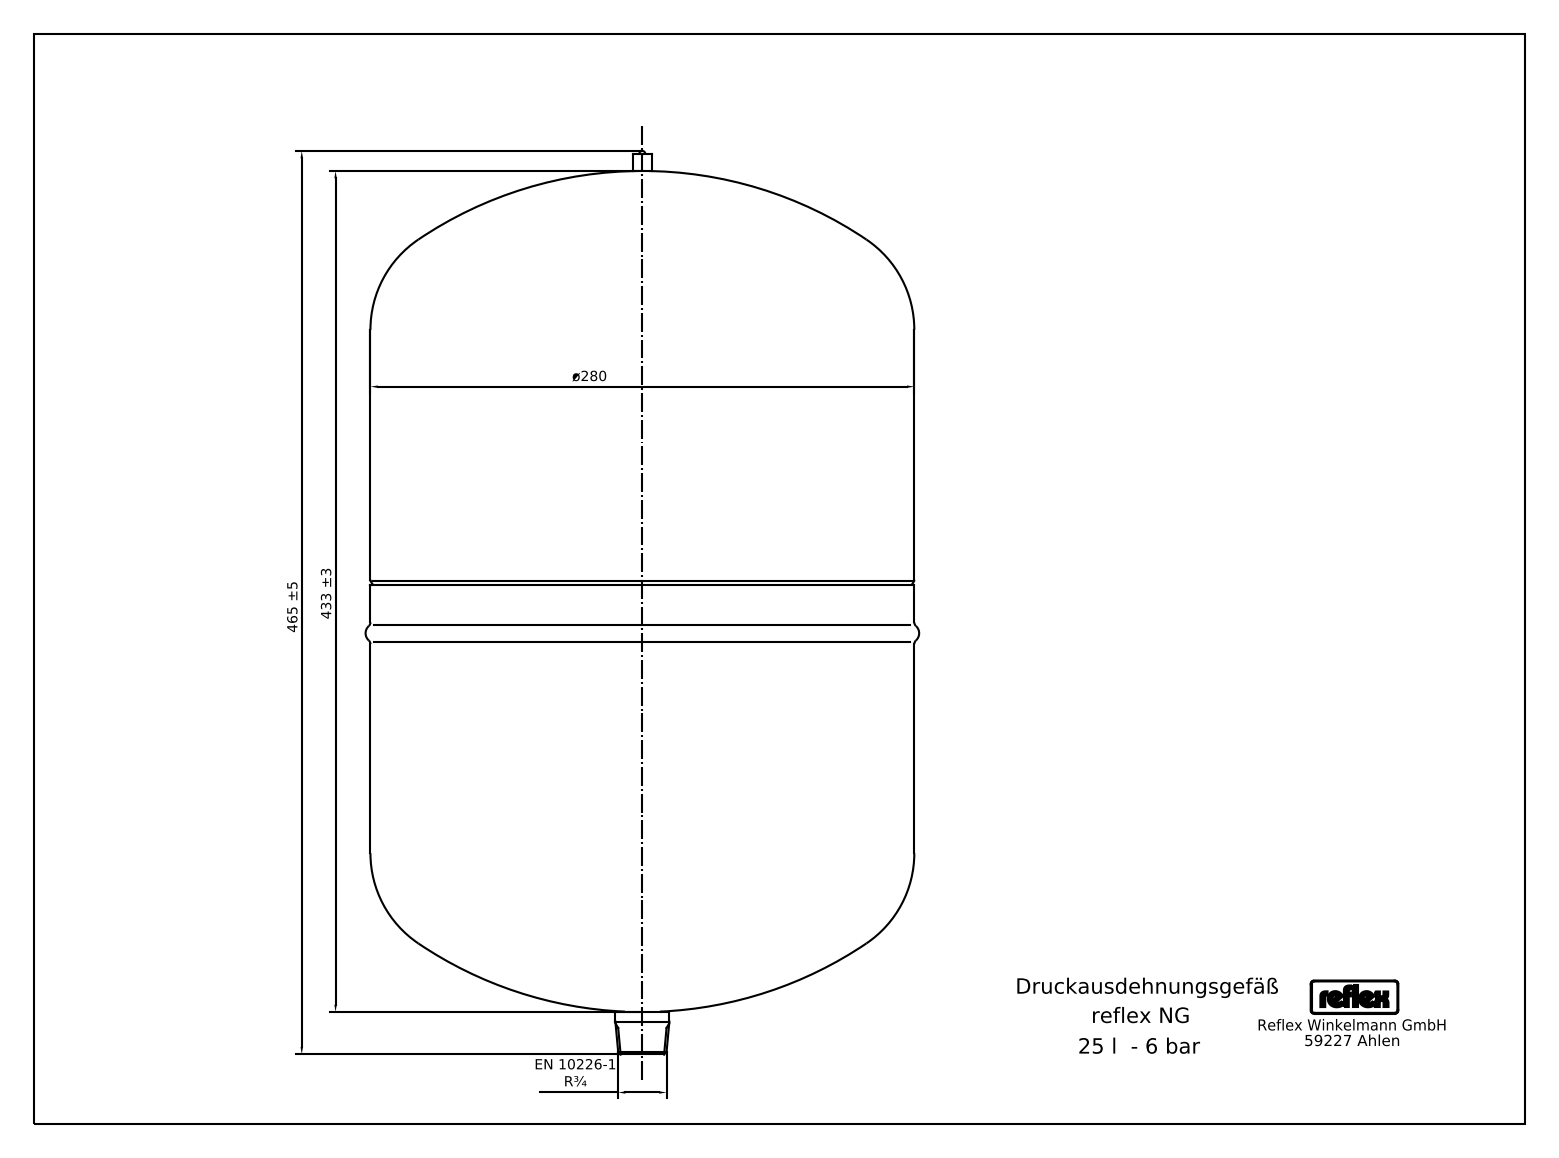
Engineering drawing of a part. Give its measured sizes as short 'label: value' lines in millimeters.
written by: Mechanical Desktop 2011 (CONFIG_CONTROL_DESIGN)
unit: mm
bodies: 13 solids, 125 faces (64 planar, 38 cylindrical, 23 other)
size: 465 × 302 × 302
volume: 24 480 000 mm³; area: 735 217 mm²
holes: 1× ⌀18.9
bosses: 1× ⌀302, 1× ⌀280, 1× ⌀26.9, 1× ⌀10, 1× ⌀6
rounds: 4× R1.12, 3× R0.45, 2× R0.77, 2× R1.35, 2× R1.85, 2× R1.88, 2× R2.54, 1× R0.56
face distances: 324, 154, 170, 16, 20, 74, 228, 244, 398, 54
